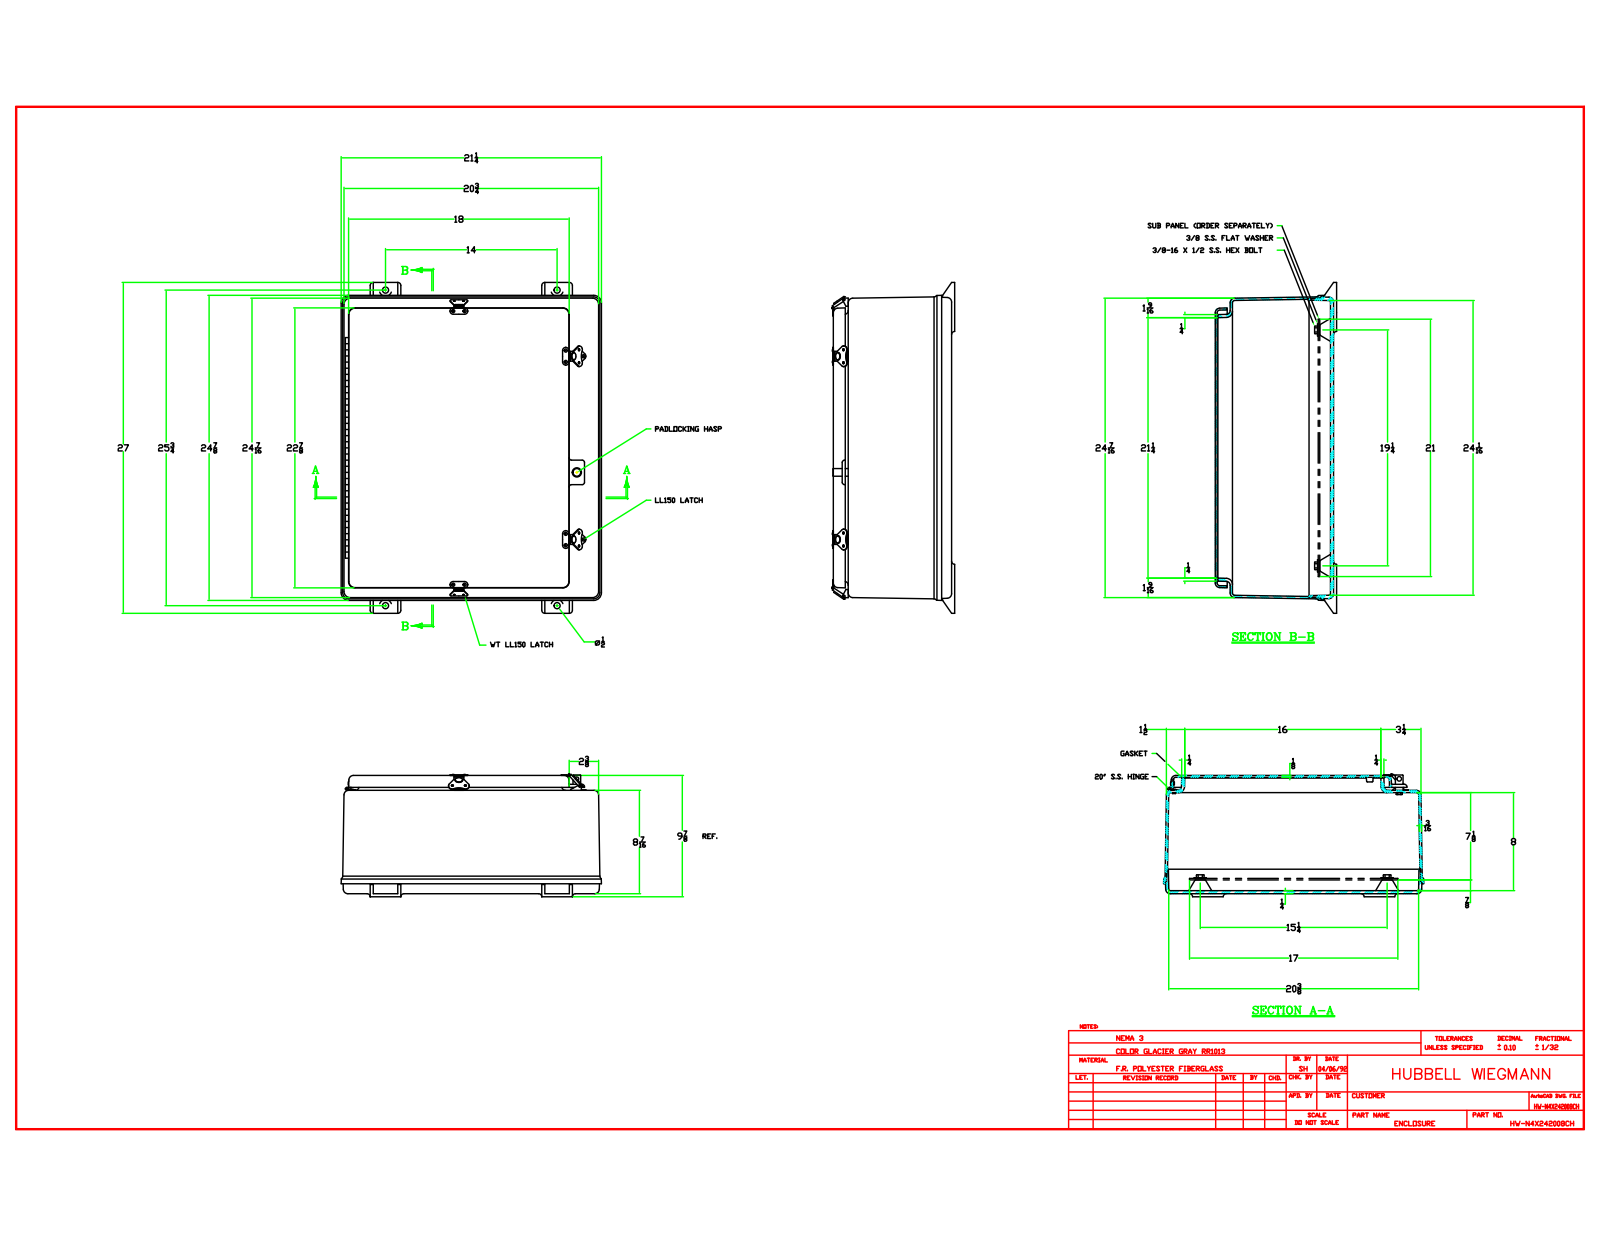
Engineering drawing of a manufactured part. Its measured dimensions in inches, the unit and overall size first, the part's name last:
Units: inches
Overall size (bounding box): 27 × 21.25 × 10.239
Round holes (diameter × count): ⌀0.13 ×34, ⌀0.063 ×16, ⌀0.065 ×8, ⌀0.138 ×8, ⌀0.187 ×8, ⌀0.281 ×4, ⌀0.563 ×4, ⌀0.135 ×3, ⌀0.156 ×3, ⌀0.145 ×2, ⌀0.51 ×2, ⌀0.51 ×2
Round bosses / shafts (diameter × count): ⌀0.14 ×16, ⌀0.297 ×8, ⌀0.5 ×4, ⌀0.2 ×3, ⌀0.25 ×1, ⌀0.201 ×1
Partial cylindrical surfaces — rounded edges, fillets, slot ends (radius × count): R0.01 ×101, R0.25 ×24, R0.187 ×21, R0.03 ×16, R0.313 ×16, R0.375 ×16, R0.5 ×12, R0.063 ×10
Main face-to-face distances: 0.25, 0.186, 9.657, 9.407, 0.156, 9.5, 9.25, 8.436, 8.25, 8
Hole centre spacings: 0.5, 5.25, 1, 3.309, 11.75, 14.938, 14.981, 22.508
Volume: 410.2 in³ · Surface area: 4 352 in²
Bodies: 56 solids, 1513 faces (578 planar, 594 cylindrical, 341 other)
Part name (STEP PRODUCT): WPN24208SHWT; WPN2420B; WPN24208HWTPCVR; N24208G (+8 more)
STEP written by: Autodesk Inventor 2014 (AUTOMOTIVE_DESIGN)
